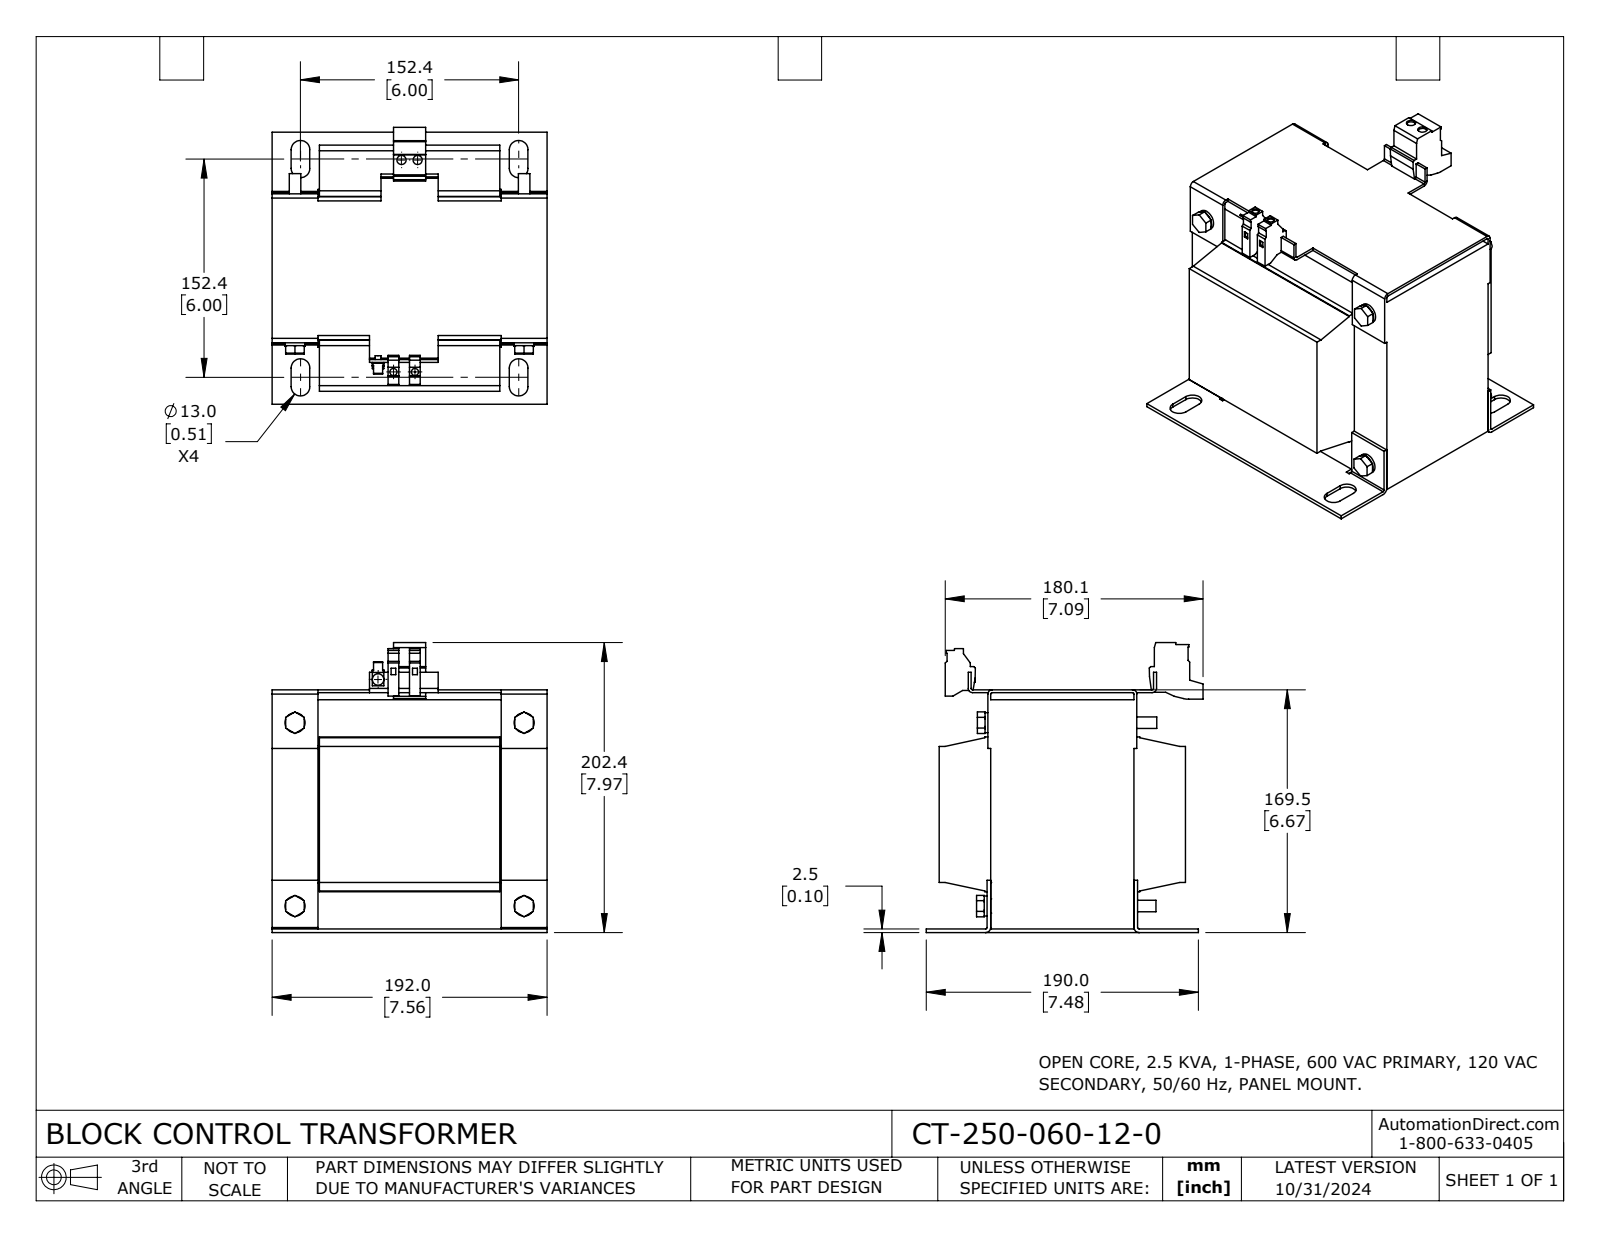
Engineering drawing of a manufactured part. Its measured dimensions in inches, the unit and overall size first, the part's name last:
Units: inches
Overall size (bounding box): 7.969 × 7.61 × 7.559
Round holes (diameter × count): ⌀0.197 ×2, ⌀0.252 ×2
Round bosses / shafts (diameter × count): ⌀0.315 ×5, ⌀0.551 ×4, ⌀0.394 ×2, ⌀0.157 ×1
Partial cylindrical surfaces — rounded edges, fillets, slot ends (radius × count): R0.256 ×8, R0.039 ×6, R0.118 ×4, R0.138 ×2, R0.591 ×1
Main face-to-face distances: 6.299, 1.299, 6.26, 1.26, 0.098, 0.079, 1.417, 5.354, 5.039, 0.039
Hole centre spacings: 0.443, 0.591, 5.827, 5.831, 5.839, 5.865
Volume: 252.3 in³ · Surface area: 514.3 in²
Bodies: 1 solid, 377 faces (303 planar, 74 cylindrical, 0 other)
Part name (STEP PRODUCT): CT-250-060-12-0
STEP written by: SolidWorks 2023 (CONFIG_CONTROL_DESIGN)
